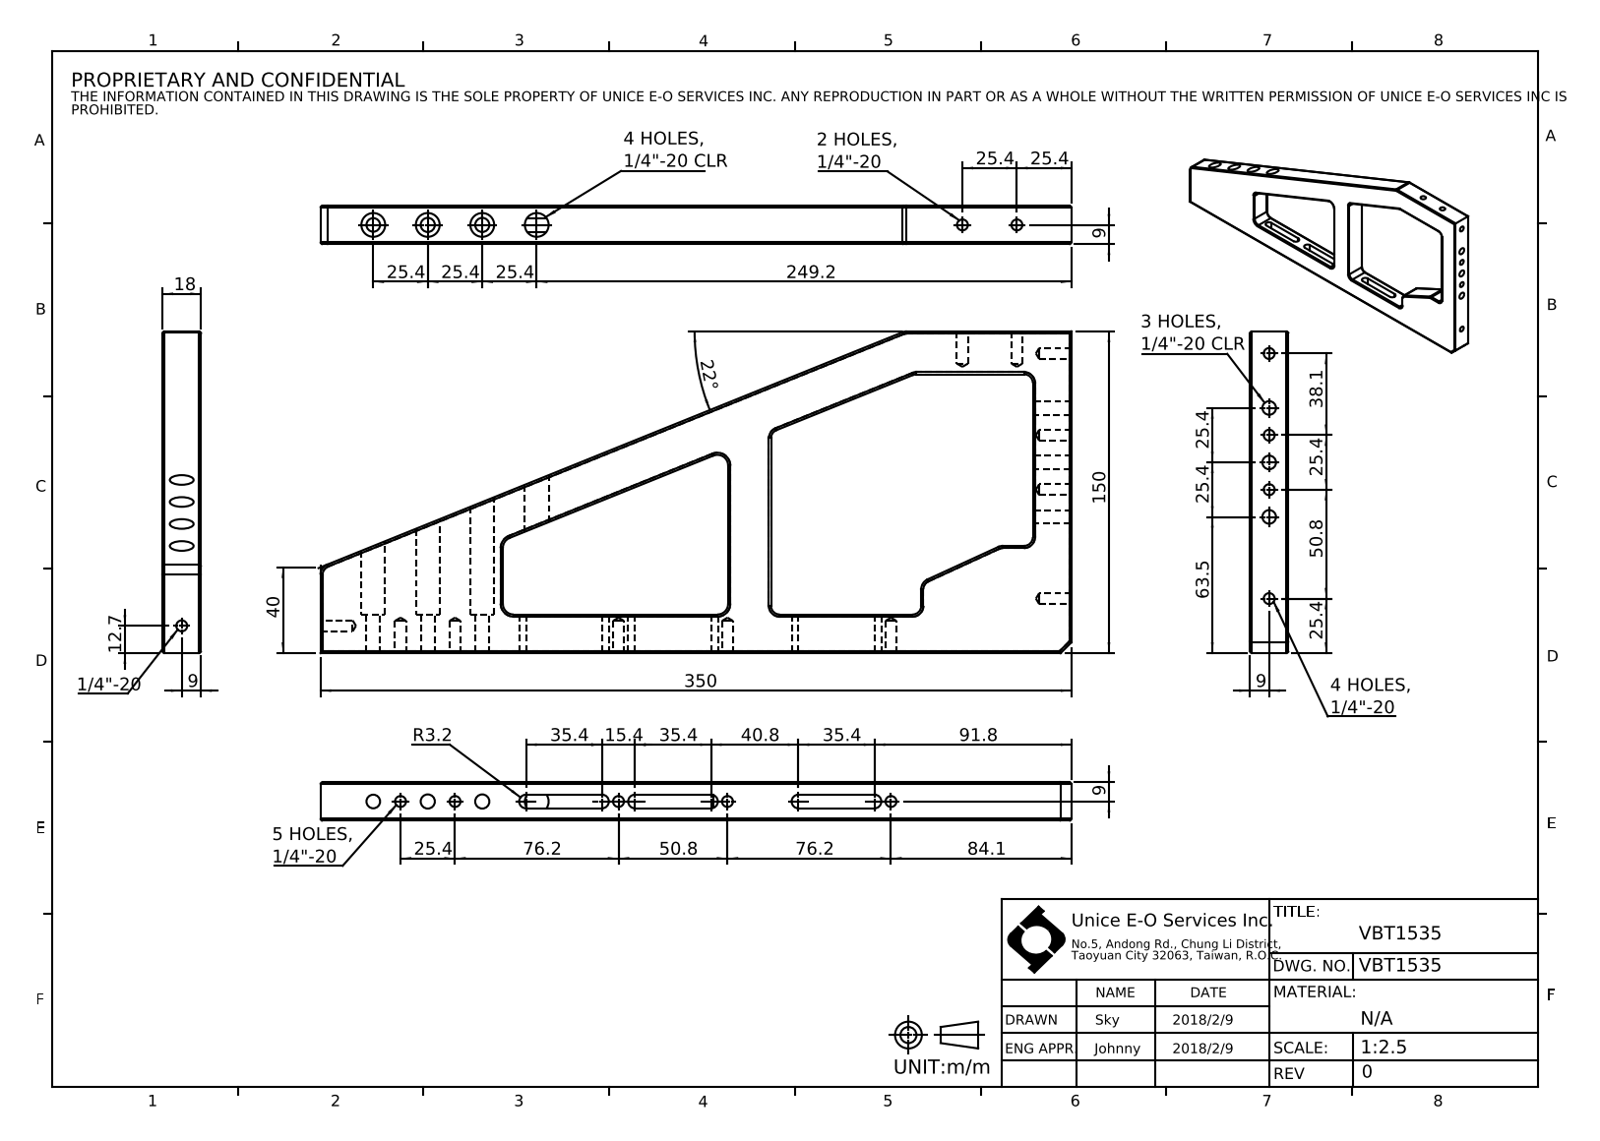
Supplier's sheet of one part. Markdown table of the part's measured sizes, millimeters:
| quantity | value |
| --- | --- |
| part name | U-F1-VBT1535-1-DP; VBT1535 |
| STEP written by | SolidWorks 2016 (AUTOMOTIVE_DESIGN) |
| units | millimeters |
| bodies | 1 solid, 182 faces (29 planar, 101 cylindrical, 52 other) |
| overall size | 350 × 150 × 18 |
| volume | 329 024 mm³ |
| surface area | 81 937 mm² |
| round holes (diameter × count) | 5.11 × 12, 6.35 × 4, 11.1 × 4, 6.6 × 2 |
| partial cylindrical surfaces (radius × count) | 1 × 33, 5 × 8, 3.2 × 6, 4 × 6 |
| main face-to-face distances | 18, 5.8, 12.2, 6.4, 20, 20.4, 140, 132, 150, 20.44 |
| hole center spacings | 12.7, 25.4, 38.1, 50.8, 76.2, 63.5, 88.9, 114.3 |
